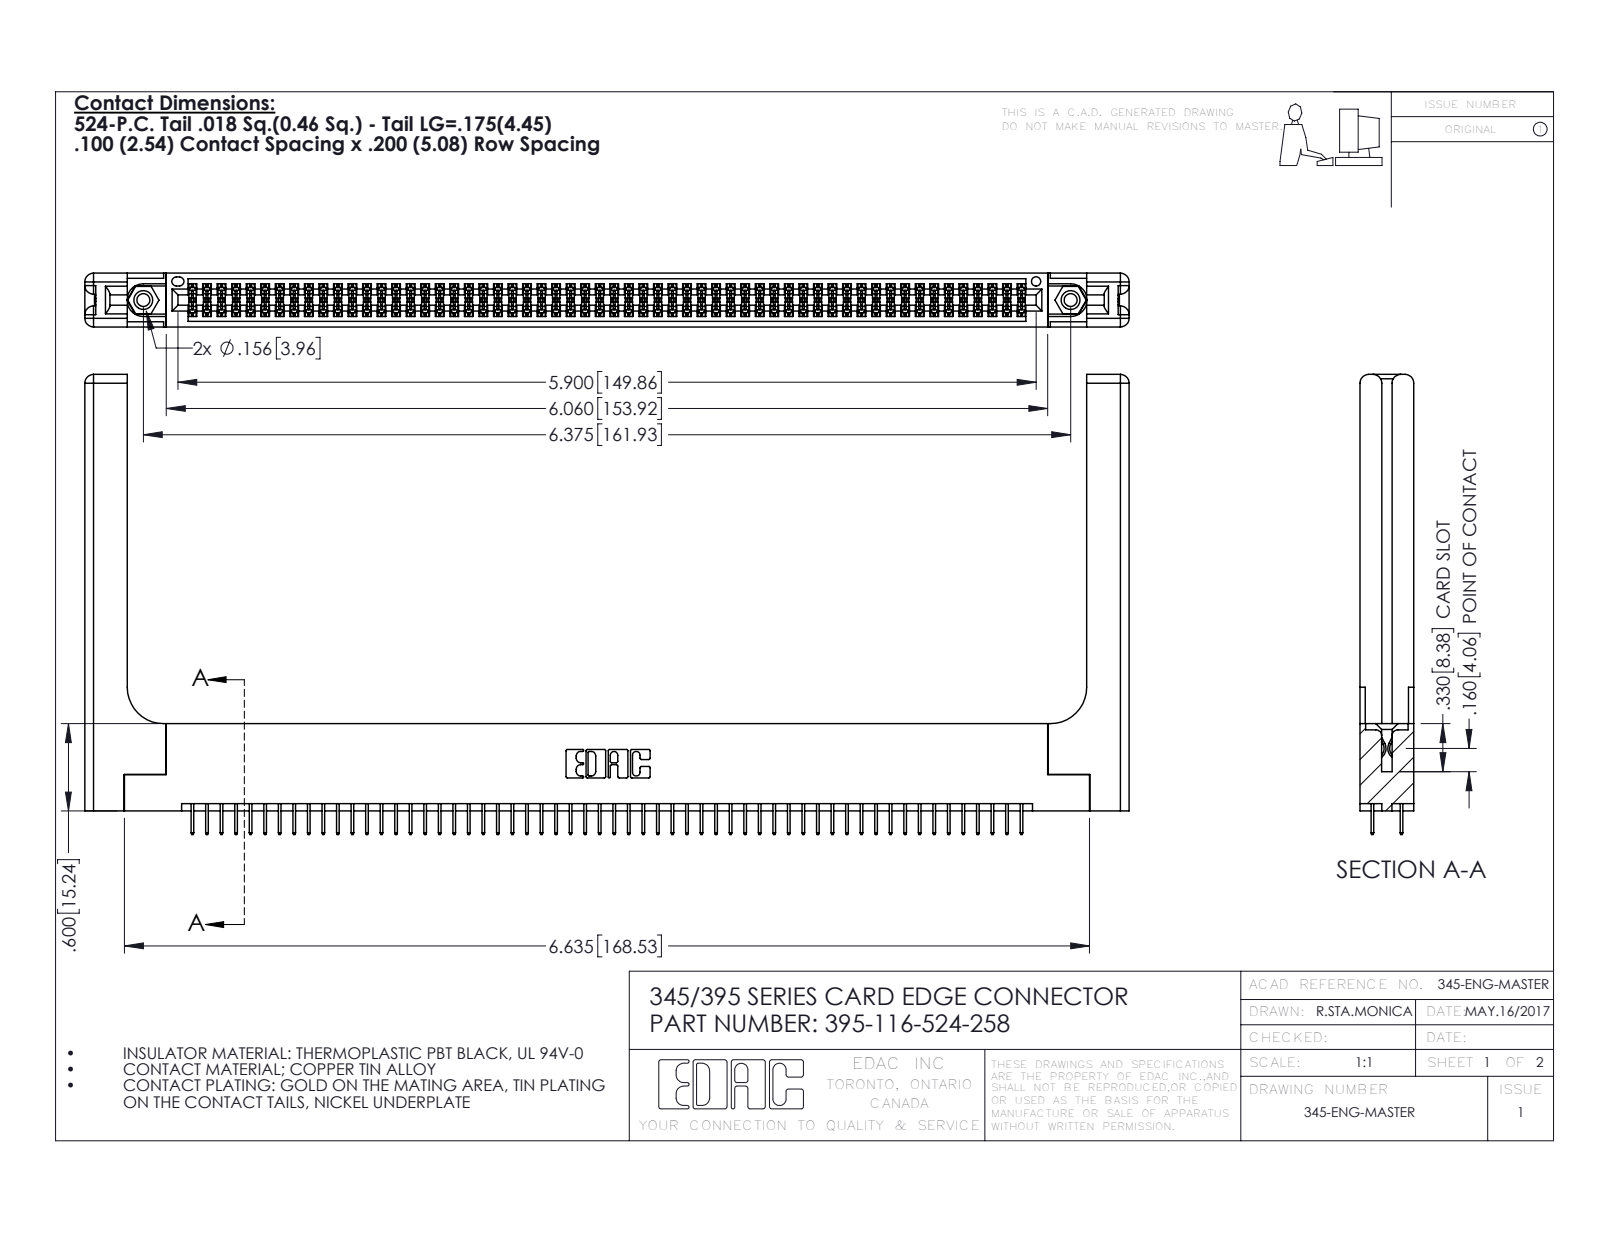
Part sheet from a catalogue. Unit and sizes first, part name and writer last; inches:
Units: inches
Overall size (bounding box): 7.179 × 3.162 × 0.37
Round holes (diameter × count): ⌀0.089 ×2, ⌀0.125 ×2, ⌀0.156 ×2, ⌀0.064 ×1
Round bosses / shafts (diameter × count): ⌀0.155 ×2
Partial cylindrical surfaces — rounded edges, fillets, slot ends (radius × count): R0.006 ×174, R0.01 ×22, R0.06 ×16, R0.007 ×6, R0.031 ×6, R0.026 ×3, R0.014 ×2, R0.019 ×2
Main face-to-face distances: 0.072, 0.298, 0.37, 0.2, 0.098, 0.272, 0.025, 0.225, 0.148, 0.15
Hole centre spacings: 0.27, 6.139, 6.375
Volume: 1.596 in³ · Surface area: 48.13 in²
Bodies: 121 solids, 6646 faces (4752 planar, 1834 cylindrical, 60 other)
Part name (STEP PRODUCT): 395-116-524-258; 345-250-001_345-250-001-102; 345-292-001_345-293-124; 345-220-058_345-220-058 (+1 more)
STEP written by: SolidWorks 2016 (CONFIG_CONTROL_DESIGN)
